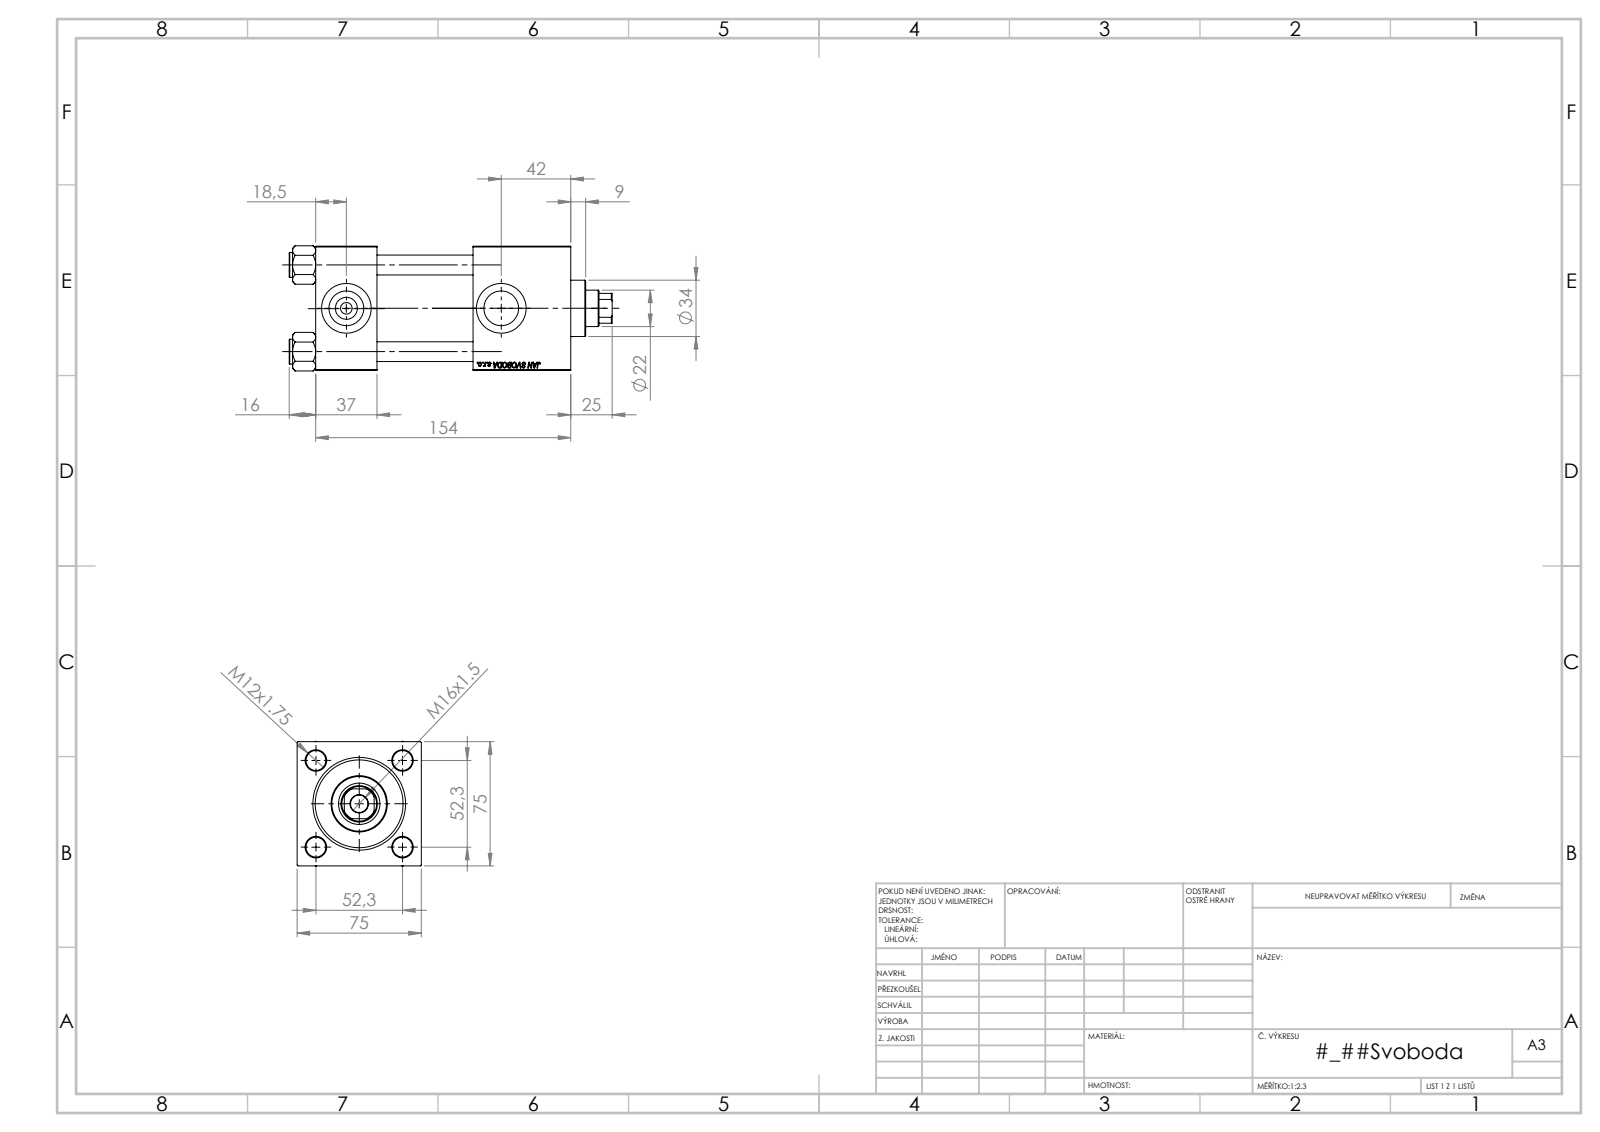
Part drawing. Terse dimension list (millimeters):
name: V215CD_VC_C; V215CD_VCP_C; NUT_M5_V215CD_C; V215CD_Body_C (+1 more)
written by: SolidWorks 2019 (CONFIG_CONTROL_DESIGN)
unit: mm
bodies: 11 solids, 1148 faces (526 planar, 86 cylindrical, 536 other)
size: 195 × 75.54 × 75
volume: 656 964 mm³; area: 147 285 mm²
holes: 4× ⌀12, 2× ⌀7, 2× ⌀20.96, 2× ⌀30, 1× ⌀10.5, 1× ⌀22, 1× ⌀25, 1× ⌀41, 1× ⌀50, 1× ⌀53
bosses: 4× ⌀15, 1× ⌀56, 1× ⌀34
rounds: 1× R10.5
face distances: 75, 37, 154, 117, 95, 58, 59, 125.3, 88.3, 30.3
hole spacings: 36.98, 52.3, 73.96, 93.5
